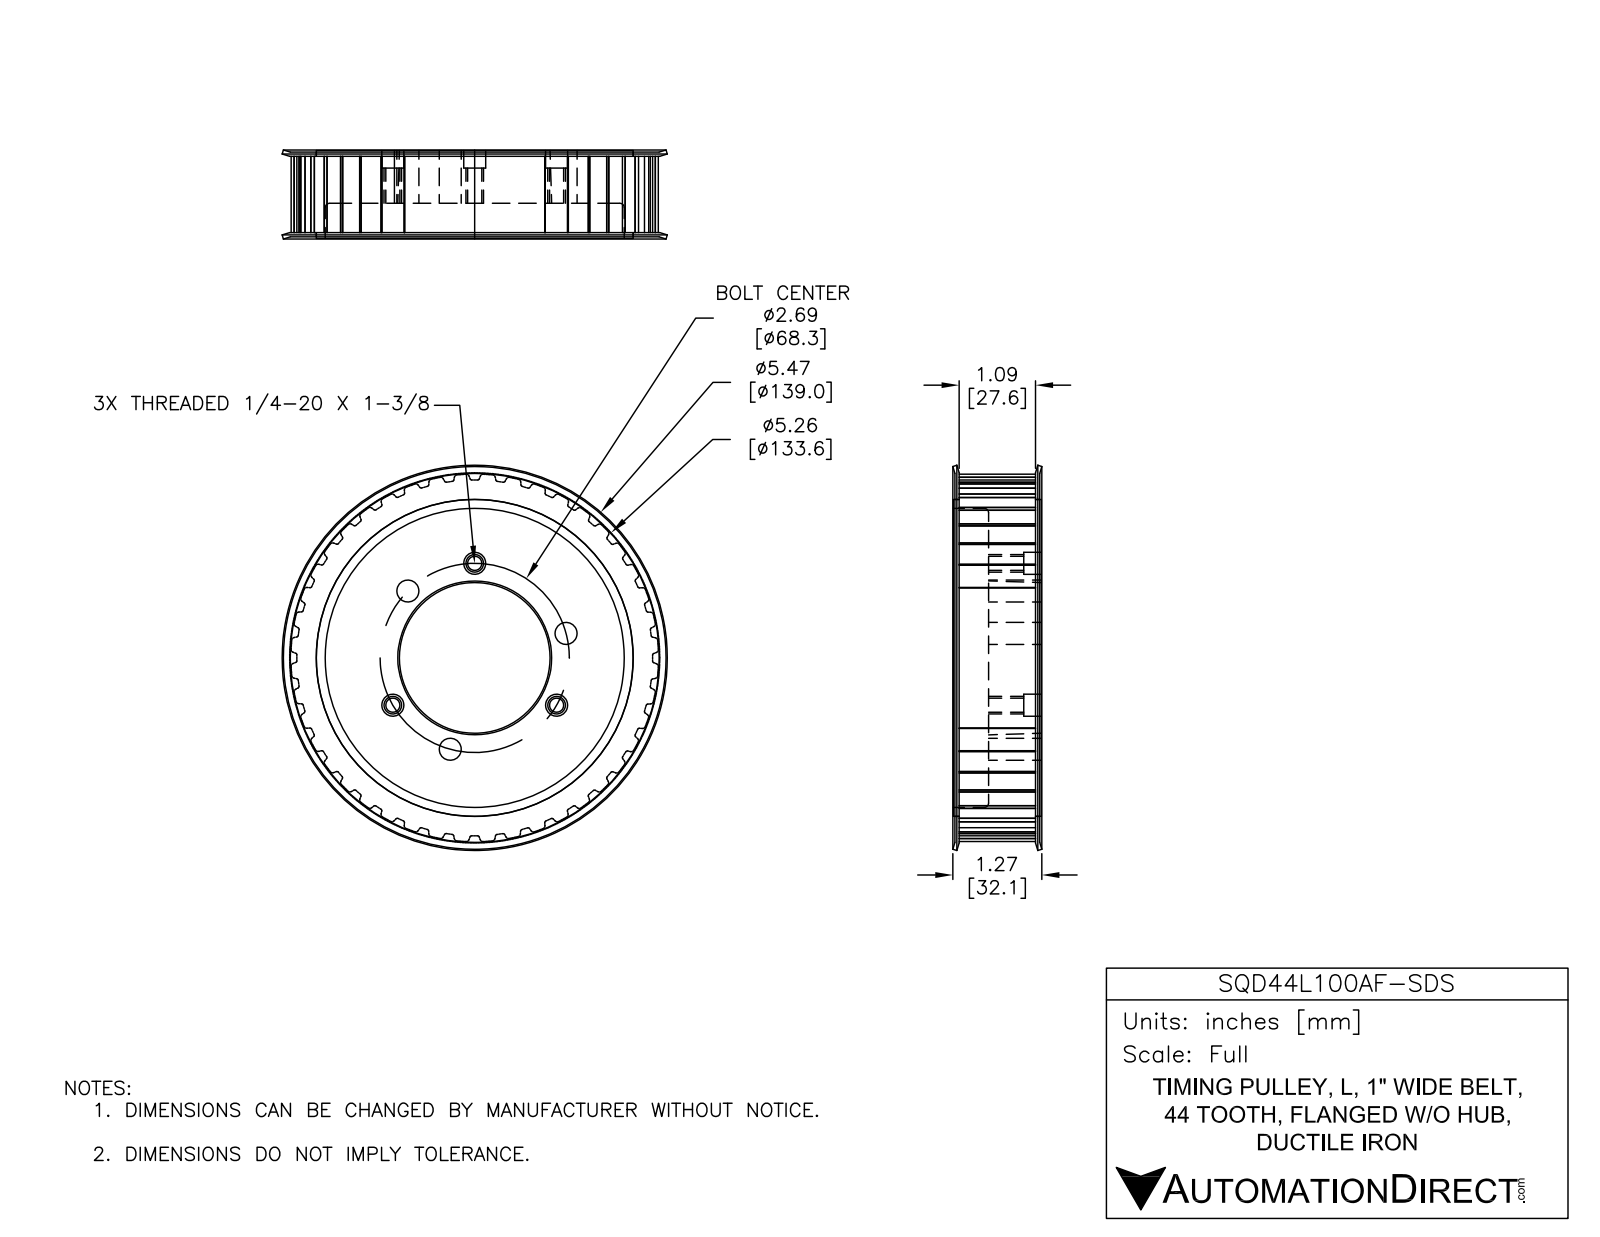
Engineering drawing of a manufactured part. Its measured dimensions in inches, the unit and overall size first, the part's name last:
Units: inches
Overall size (bounding box): 5.474 × 5.474 × 1.265
Round holes (diameter × count): ⌀0.313 ×6, ⌀0.201 ×3, ⌀4.25 ×1, ⌀4.504 ×1
Round bosses / shafts (diameter × count): ⌀4.5 ×1
Partial cylindrical surfaces — rounded edges, fillets, slot ends (radius × count): R0.021 ×84, R0.04 ×84, R2.612 ×1
Main face-to-face distances: 0.75, 0.023, 1.228, 0.727, 1.205, 0.478, 0.5, 0.06, 1.145, 1.25
Hole centre spacings: 1.344, 2.327, 2.328, 2.665, 1.028, 1.636, 1.029, 1.343
Volume: 16.06 in³ · Surface area: 87.74 in²
Bodies: 1 solid, 434 faces (144 planar, 274 cylindrical, 16 other)
Part name (STEP PRODUCT): SQD44L100AF-SDS
STEP written by: SolidWorks 2018 (AUTOMOTIVE_DESIGN)
